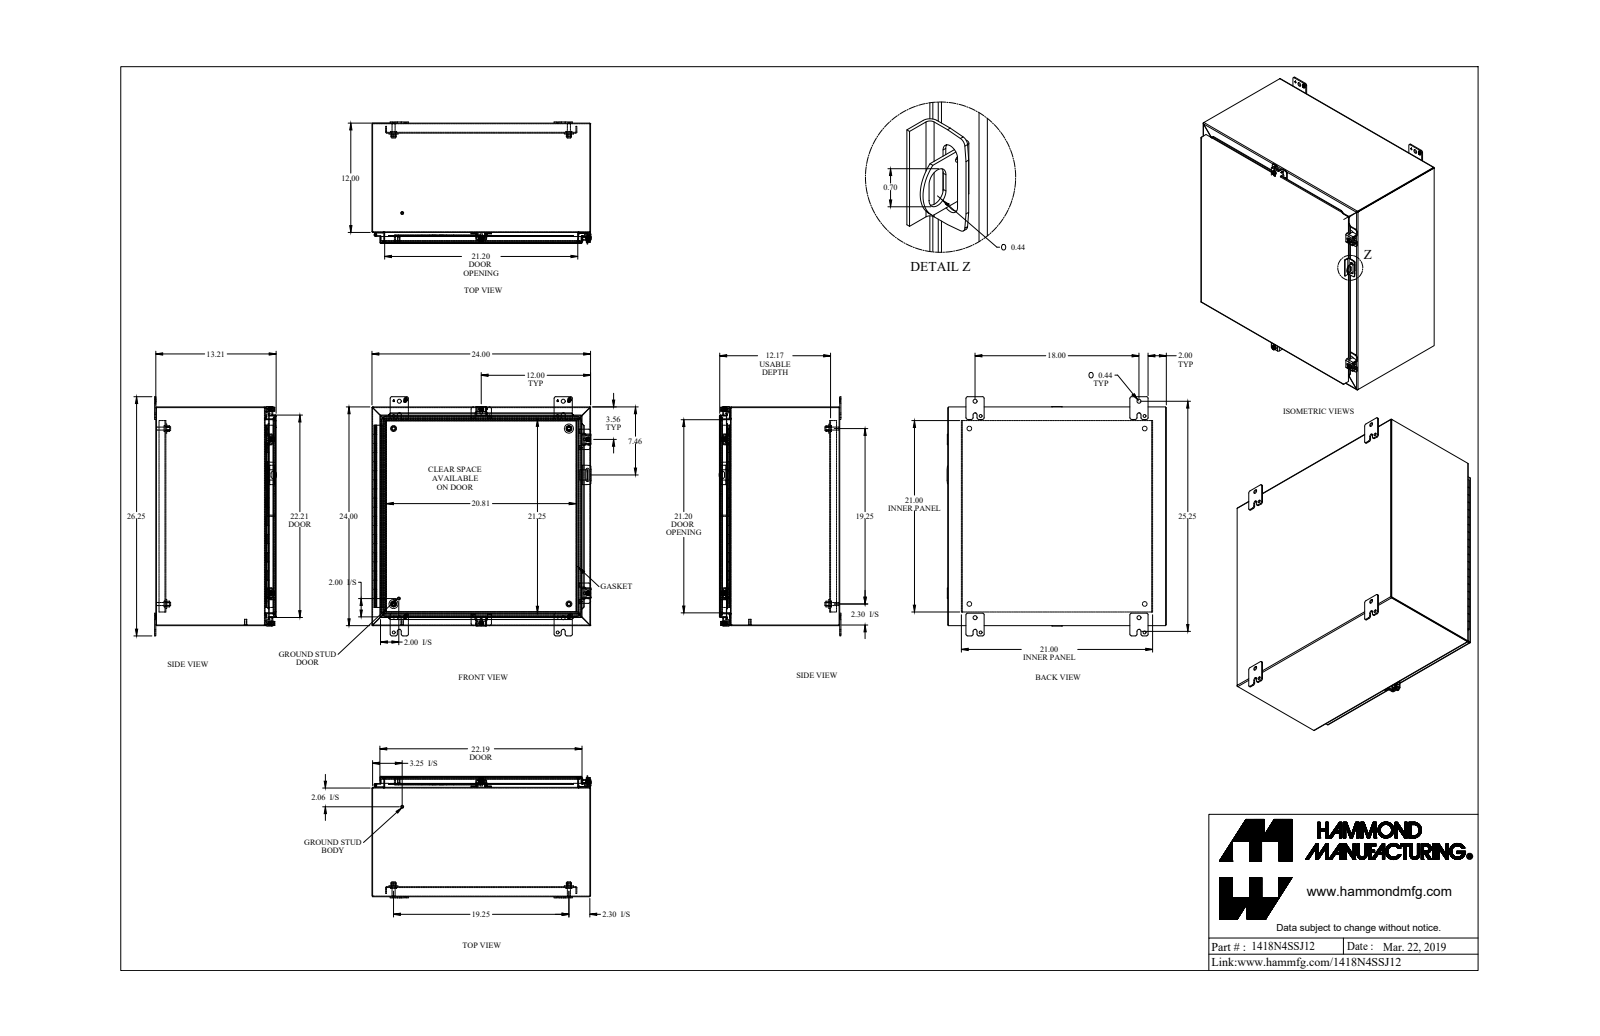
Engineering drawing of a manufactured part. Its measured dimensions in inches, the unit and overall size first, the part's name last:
Units: inches
Overall size (bounding box): 26.25 × 24.063 × 13.492
Round holes (diameter × count): ⌀0.213 ×4, ⌀0.265 ×4, ⌀0.313 ×4, ⌀0.375 ×4, ⌀0.437 ×4, ⌀0.5 ×4, ⌀0.307 ×2, ⌀0.445 ×2, ⌀0.125 ×1, ⌀0.187 ×1, ⌀0.196 ×1, ⌀0.25 ×1
Round bosses / shafts (diameter × count): ⌀0.65 ×4, ⌀0.5 ×4, ⌀0.39 ×4, ⌀0.375 ×4, ⌀0.332 ×4, ⌀0.244 ×4, ⌀1 ×2, ⌀0.313 ×2
Partial cylindrical surfaces — rounded edges, fillets, slot ends (radius × count): R0.188 ×26, R0.036 ×22, R0.108 ×22, R0.048 ×21, R0.143 ×21, R0.25 ×20, R0.125 ×10, R0.045 ×8
Main face-to-face distances: 0.072, 23.928, 23.856, 24, 0.072, 13.066, 13.138, 13.138, 13.21, 0.095
Hole centre spacings: 19.25, 18, 1.735, 2.434, 3.065, 9.857, 9.857, 20.759
Volume: 240.7 in³ · Surface area: 6 378 in²
Bodies: 43 solids, 1505 faces (932 planar, 475 cylindrical, 98 other)
Part name (STEP PRODUCT): 1418N4SSJ12_Default
STEP written by: SolidWorks 2019 (CONFIG_CONTROL_DESIGN)
